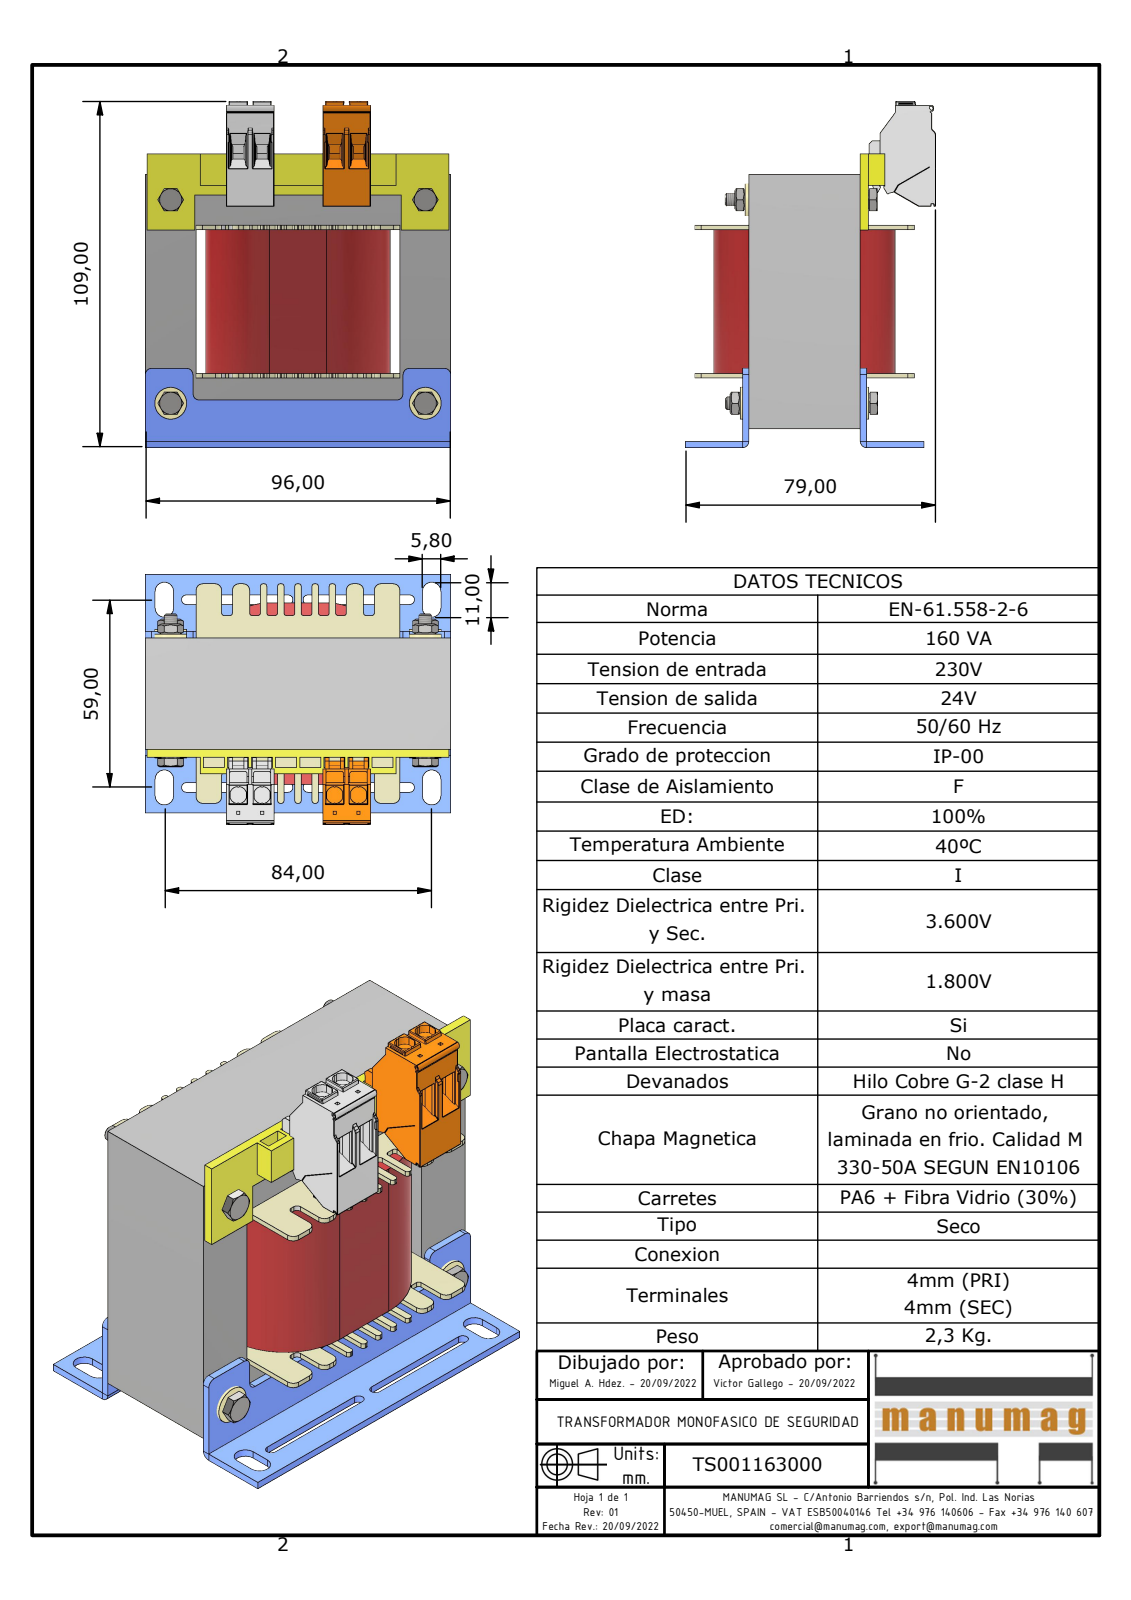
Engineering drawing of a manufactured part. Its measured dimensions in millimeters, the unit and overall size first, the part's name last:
Units: millimetres
Overall size (bounding box): 109 × 96 × 78.7
Round holes (diameter × count): ⌀3.24 ×4, ⌀4 ×4, ⌀5.5 ×4, ⌀5.8 ×2
Round bosses / shafts (diameter × count): ⌀10 ×4, ⌀5.9 ×4, ⌀4.9 ×4, ⌀3.62 ×4
Partial cylindrical surfaces — rounded edges, fillets, slot ends (radius × count): R0.15 ×160, R0.8 ×51, R0.2 ×48, R2 ×22, R0.5 ×12, R1.5 ×8, R2.9 ×8, R0.3 ×7
Main face-to-face distances: 16, 64, 32, 48, 35, 80, 2, 20, 37, 96
Hole centre spacings: 64, 80, 102.45
Volume: 333 221 mm³ · Surface area: 97 188 mm²
Bodies: 21 solids, 3890 faces (3076 planar, 574 cylindrical, 240 other)
Part name (STEP PRODUCT): TS001163000; EI96 x 80 - 35 (RC32); EI 96 X 80 - 35; EI96 (+6 more)
STEP written by: Autodesk Inventor 2023 (AUTOMOTIVE_DESIGN)
